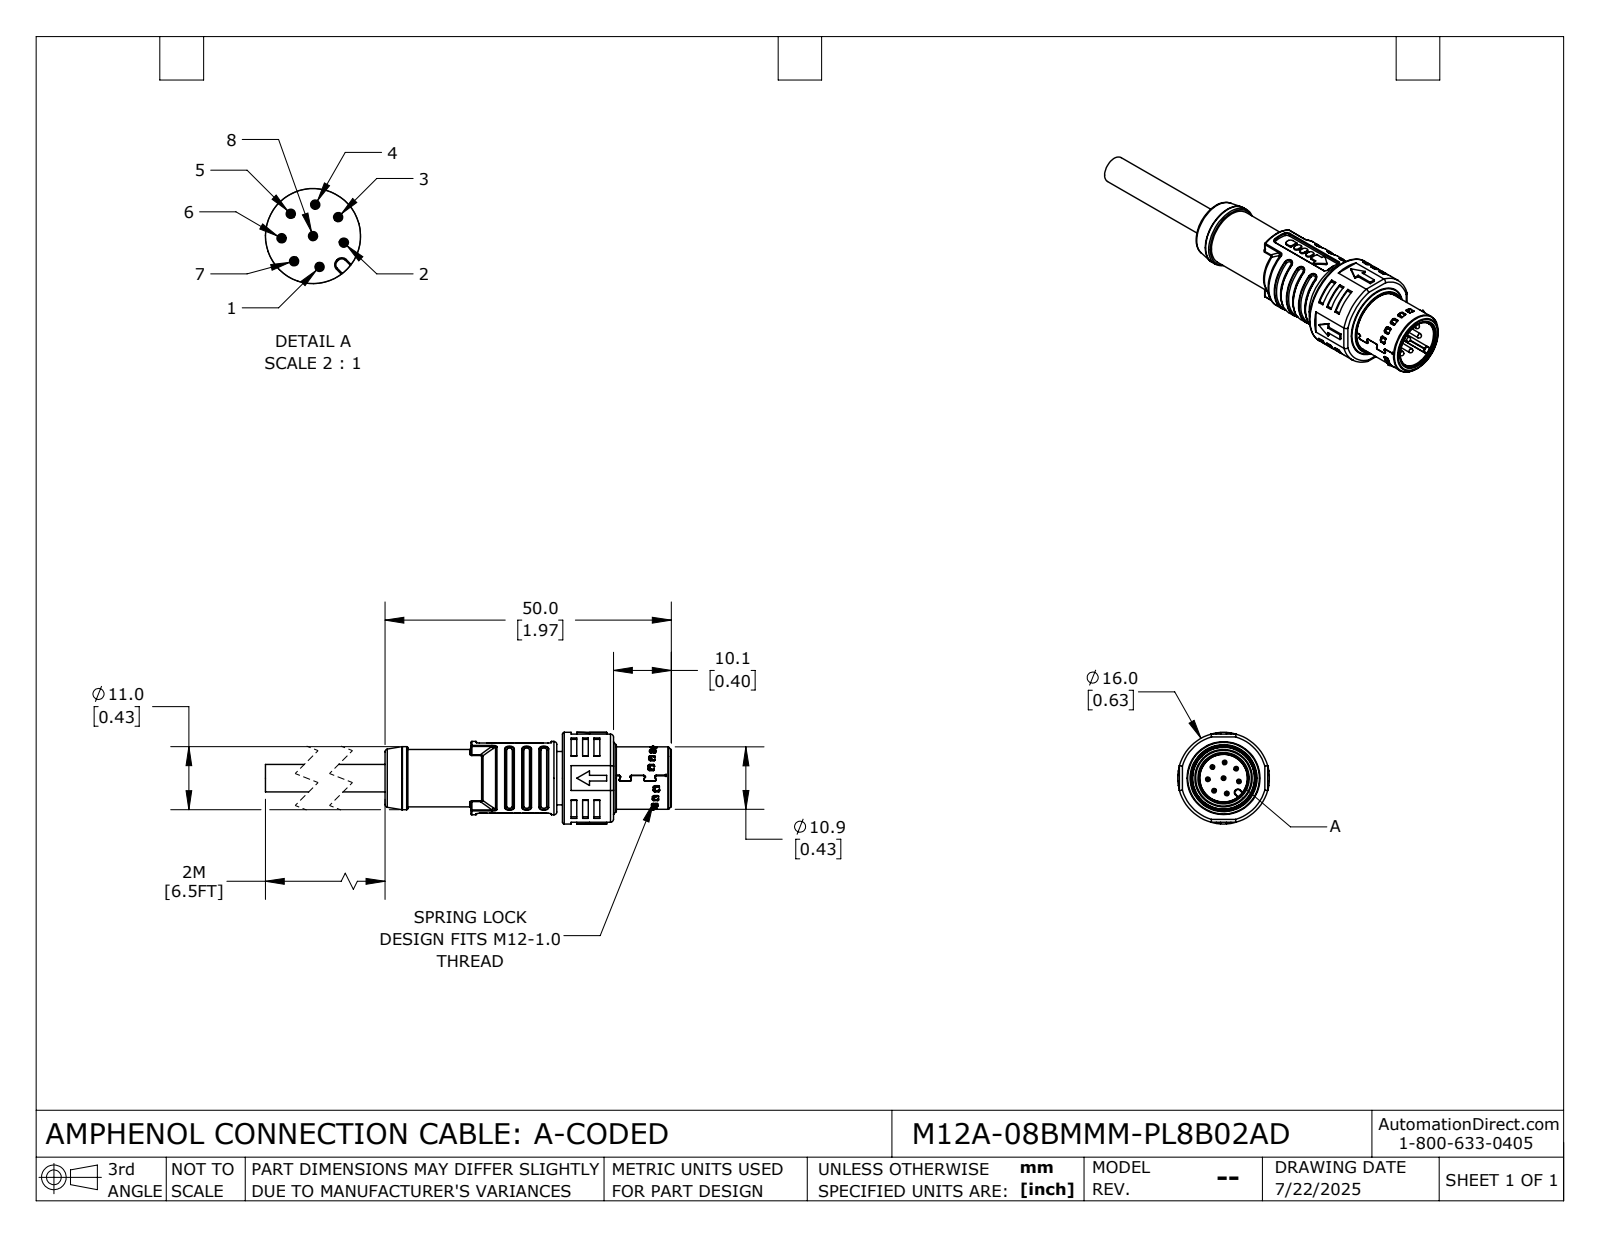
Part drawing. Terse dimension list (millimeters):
name: M12A-08BMMM-PL8B02AD
written by: SolidWorks 2024 (CONFIG_CONTROL_DESIGN)
unit: mm
bodies: 1 solid, 2027 faces (880 planar, 644 cylindrical, 503 other)
size: 75 × 16 × 16
volume: 5 223 mm³; area: 5 723 mm²
holes: 1× ⌀8.3, 1× ⌀9, 1× ⌀10.15, 1× ⌀10.5, 1× ⌀10.9, 1× ⌀11.5, 1× ⌀11.8, 1× ⌀14.2
bosses: 8× ⌀0.8, 1× ⌀16, 1× ⌀14.1, 1× ⌀12.8, 1× ⌀12.4, 1× ⌀11, 1× ⌀10.45, 1× ⌀10.4
rounds: 114× R0.2, 66× R0.25, 64× R0.3, 44× R0.15, 38× R0.5, 12× R0.13, 11× R0.7, 10× R0.1
face distances: 1, 10.1, 8.6, 8.9, 2.5, 1.5, 1.2, 32.5, 15.4, 41.1
